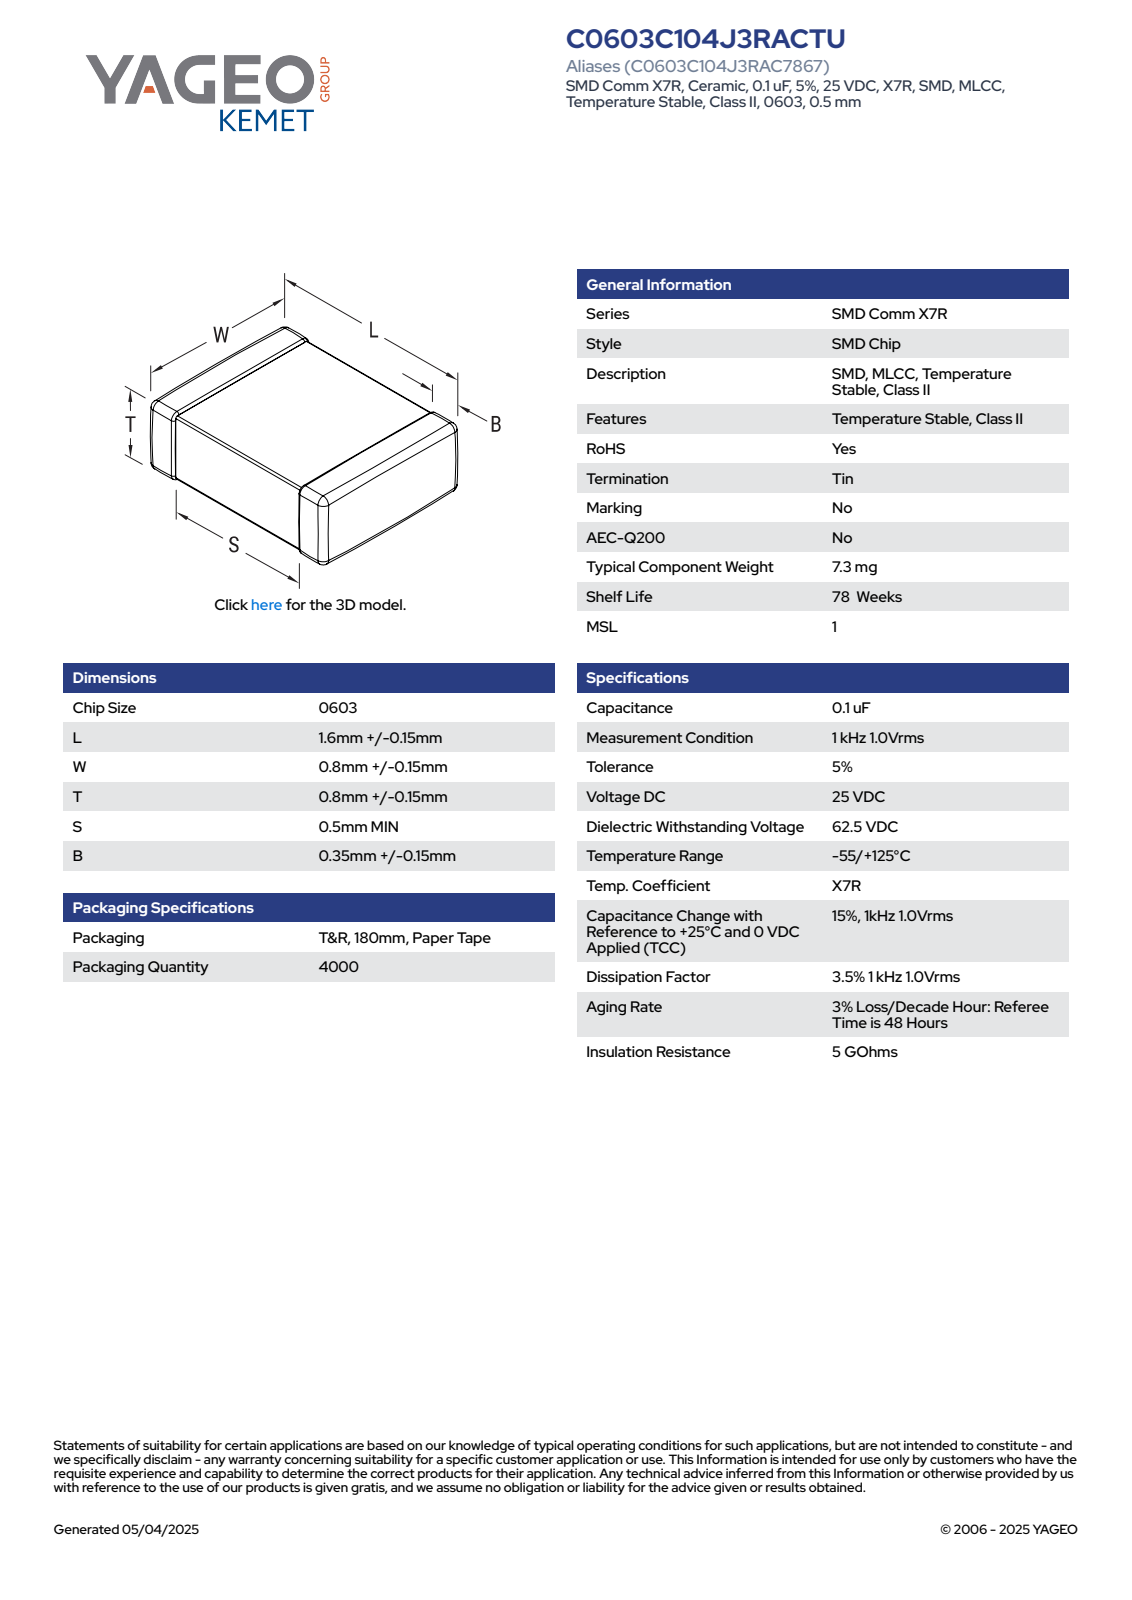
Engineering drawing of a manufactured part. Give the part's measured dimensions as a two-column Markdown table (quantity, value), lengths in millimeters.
| quantity | value |
| --- | --- |
| part name | CCS_CCSTD_0603_L1.75W0.95T0.95B0.35 |
| STEP written by | SolidWorks 2014 (AUTOMOTIVE_DESIGN) |
| units | millimeters |
| bodies | 4 solids, 125 faces (71 planar, 38 cylindrical, 16 other) |
| overall size | 1.75 × 0.95 × 0.95 |
| volume | 2 mm³ |
| surface area | 8 mm² |
| main face-to-face distances | 0.93, 0.91, 0.95, 1.75, 0.94, 0.92, 0.81, 0.8, 0.35, 0.83 |
